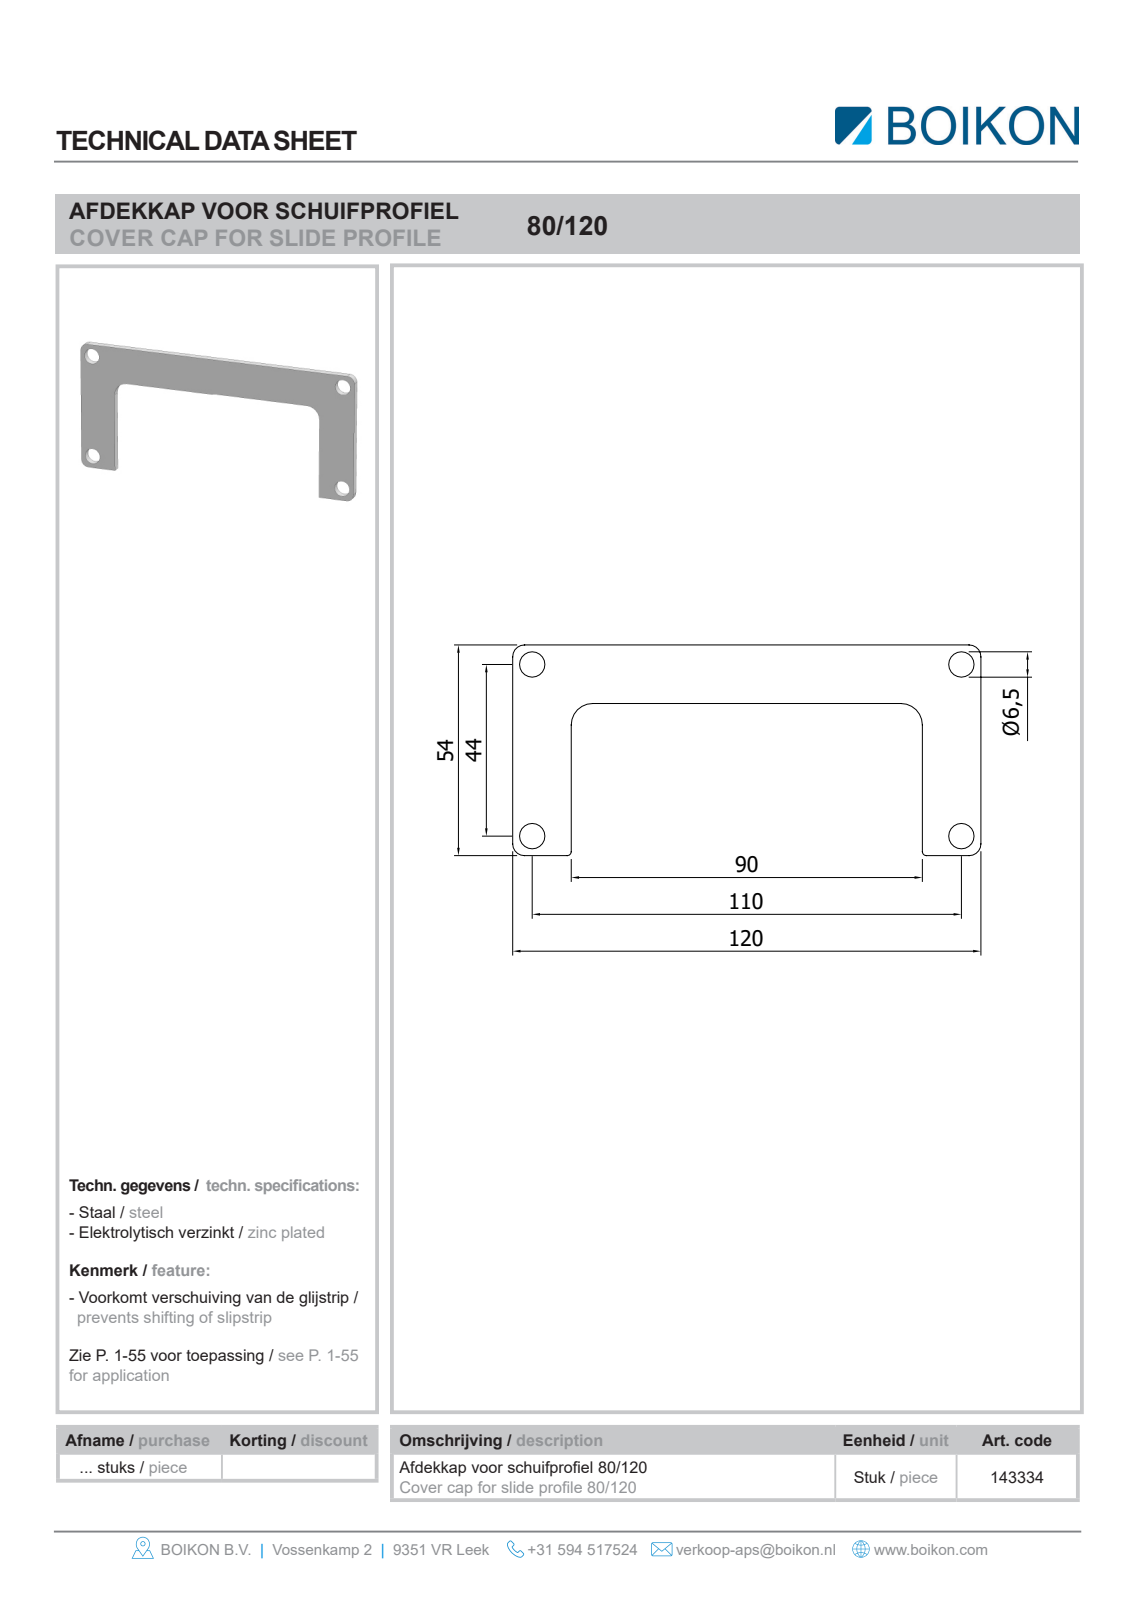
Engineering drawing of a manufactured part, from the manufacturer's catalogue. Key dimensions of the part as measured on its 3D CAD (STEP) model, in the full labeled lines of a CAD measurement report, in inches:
Part name (STEP PRODUCT): Root; 143334Afdekkap voor schuifprofiel 80-120BOIKON0; 120030Laagbolkopschroef M6 x 16Pan head bolts0
STEP written by: HiCAD 2013 1802.4 Build 509 (AUTOMOTIVE_DESIGN)
Units: inches
Bodies: 5 solids, 76 faces (50 planar, 18 cylindrical, 8 other)
Overall size (bounding box): 4.744 × 2.146 × 0.76
Volume: 0.634 in³ · Surface area: 14.14 in²
Round holes (diameter × count): ⌀0.256 ×4
Round bosses / shafts (diameter × count): ⌀0.236 ×4, ⌀0.188 ×3, ⌀0.188 ×1
Partial cylindrical surfaces — rounded edges, fillets, slot ends (radius × count): R0.118 ×4, R0.217 ×2
Main face-to-face distances: 0.118, 0.591, 4.134, 4.724, 3.543, 1.535, 2.126, 0.512, 0.63, 0.157
Hole centre spacings: 1.732, 4.331, 4.664
